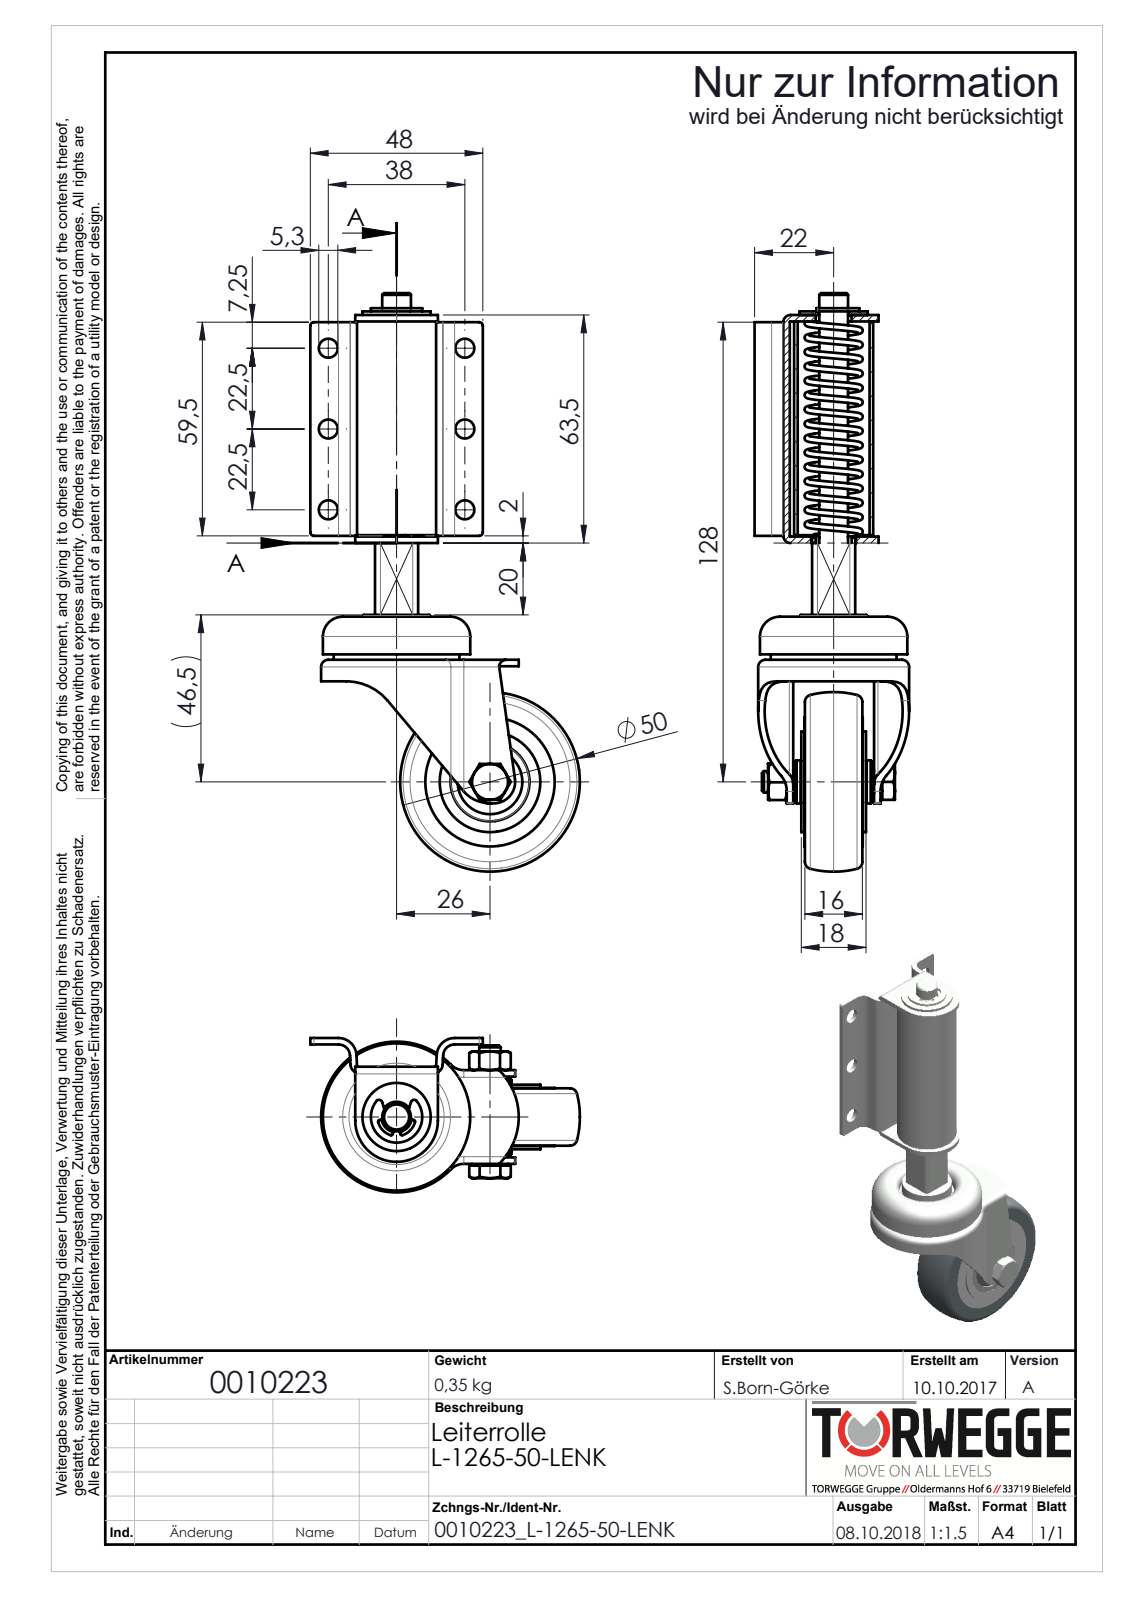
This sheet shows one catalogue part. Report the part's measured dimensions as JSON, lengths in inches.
{"part_name": "0010223_L-1265-50-LENK", "step_written_by": "SolidWorks 2018 (AUTOMOTIVE_DESIGN)", "units": "inches", "bodies": {"solids": 23, "faces": 429, "planar": 131, "cylindrical": 183, "other": 115}, "overall_size": [6.343, 2.953, 1.693], "volume_in3": 4.404, "surface_area_in2": 80.94, "round_holes": [[0.209, 6], [0.197, 1], [0.236, 1], [0.244, 1], [0.276, 1], [0.315, 1], [0.323, 1], [0.335, 1], [0.394, 1], [0.551, 1], [0.709, 1], [0.787, 1]], "round_bosses_or_shafts": [[1.614, 1], [1.417, 1], [1.378, 1], [1.102, 1], [0.866, 1], [0.748, 1], [0.728, 1], [0.492, 1]], "partial_cylinders_radius": [[0.039, 6], [0.008, 4], [0.018, 4], [0.02, 4], [0.059, 4], [0.079, 4], [0.197, 4], [0.036, 2]], "face_to_face_distances": [0.071, 0.315, 0.039, 0.433, 0.236, 0.551, 0.394, 0.63, 0.157, 0.118], "hole_center_spacings": [0.886, 1.739, 1.496, 1.772, 2.319, 2.995, 3.469, 3.878]}
